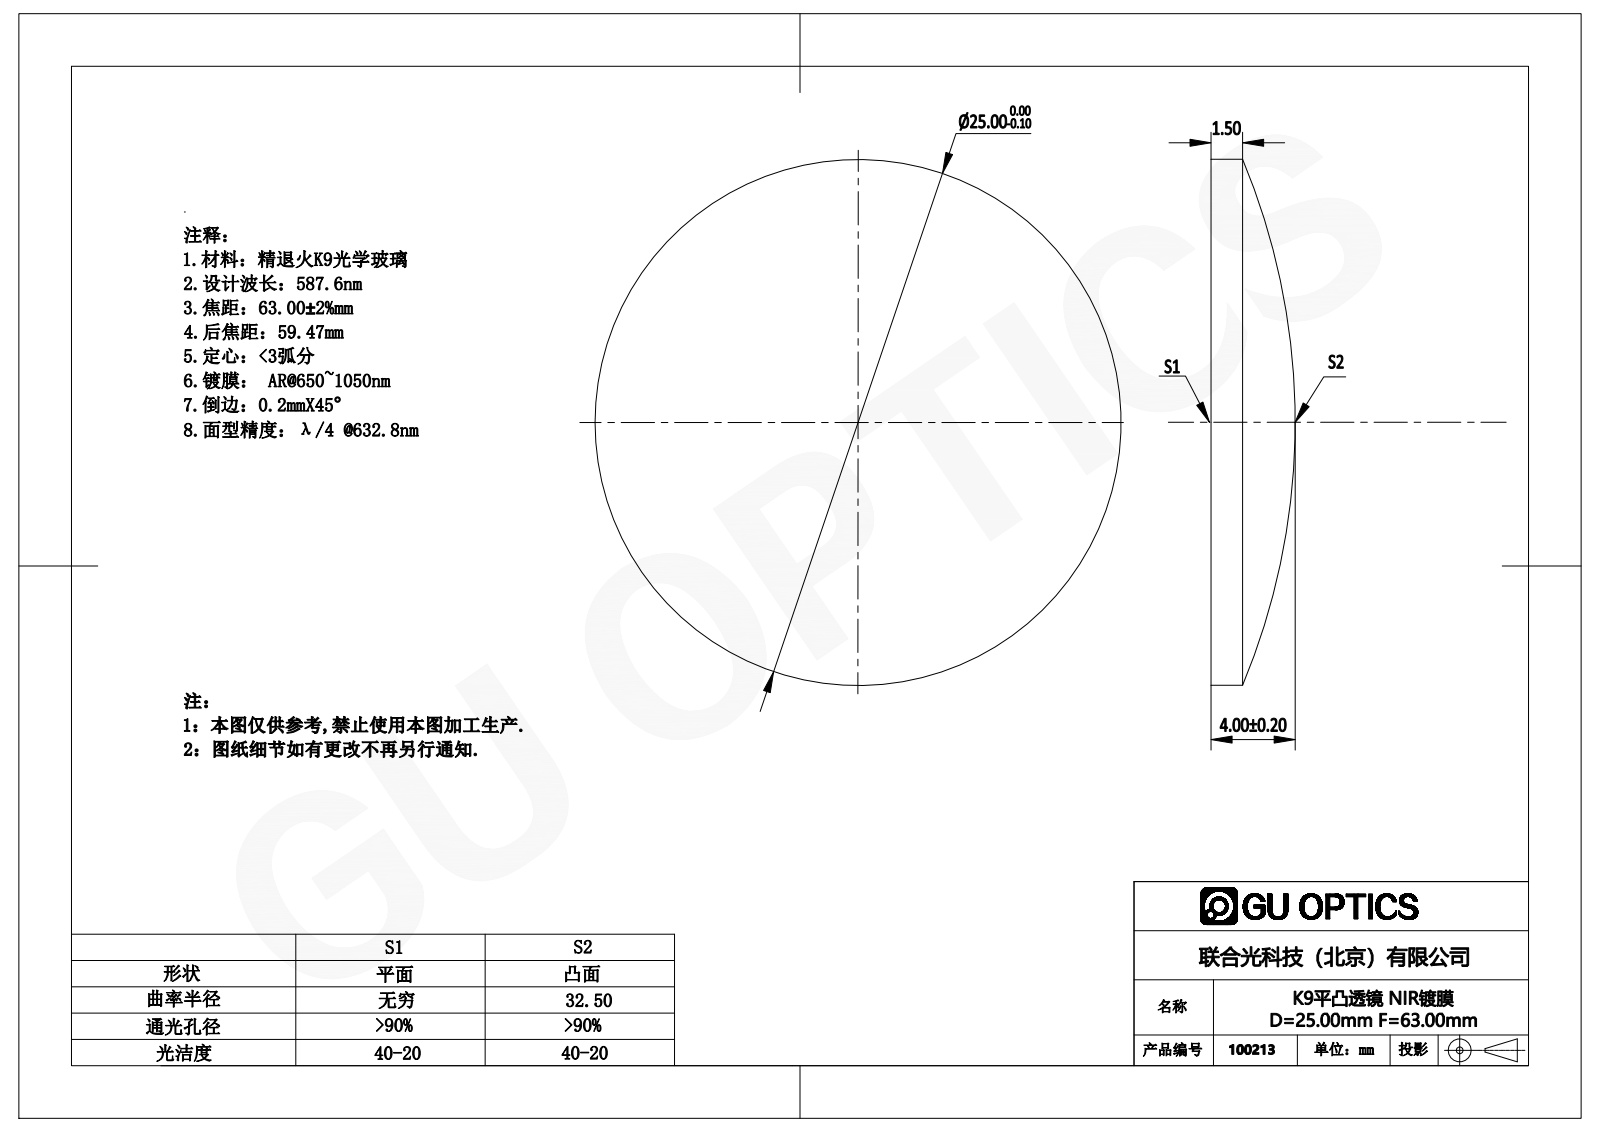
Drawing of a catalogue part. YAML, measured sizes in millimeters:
part_name: "100213"
step_written_by: "SolidWorks 2016 (AUTOMOTIVE_DESIGN)"
units: millimeters
bodies: {solids: 1, faces: 5, planar: 1, cylindrical: 2, other: 2}
overall_size: [25, 25, 4]
volume: 1358
surface_area: 1119
round_bosses_or_shafts:
  - {diameter: 25, count: 1}
